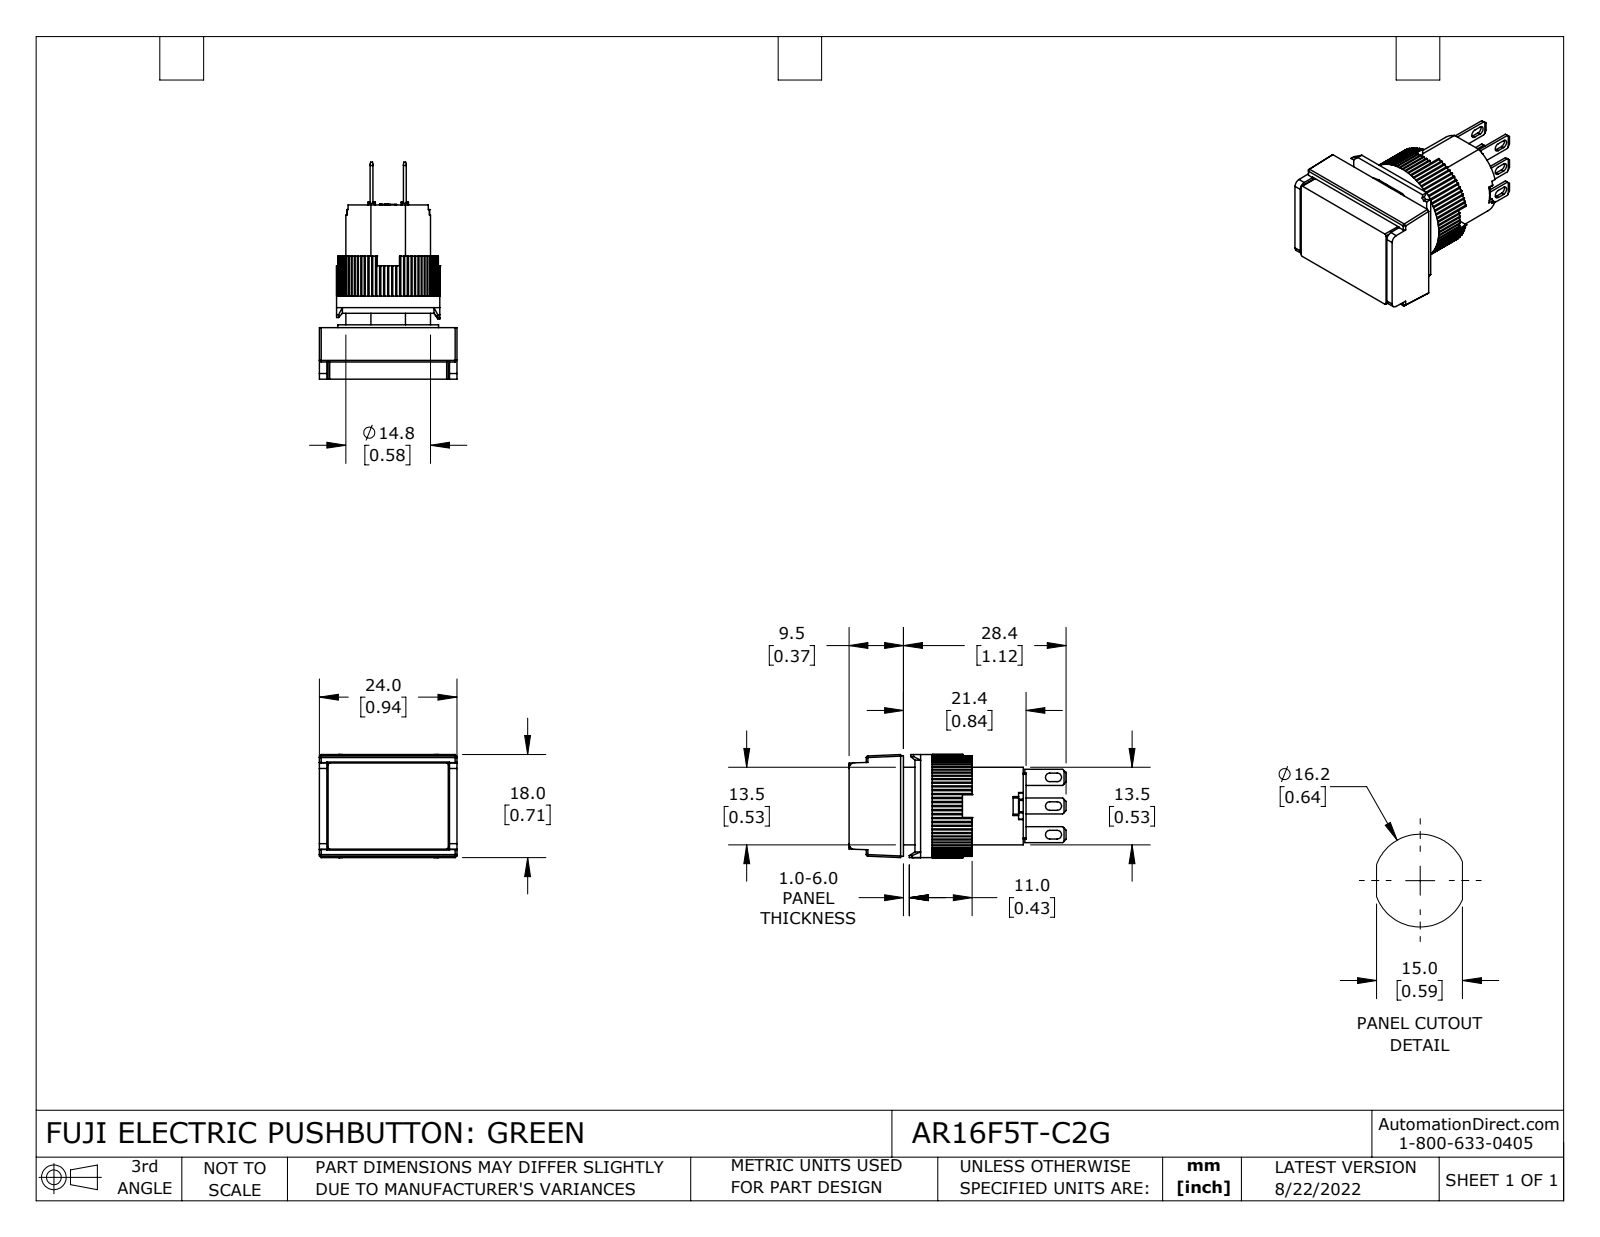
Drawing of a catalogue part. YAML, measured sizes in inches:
part_name: "AR16F5T-C2G"
step_written_by: "SolidWorks 2021 (CONFIG_CONTROL_DESIGN)"
units: inches
bodies: {solids: 12, faces: 813, planar: 632, cylindrical: 177, other: 4}
overall_size: [1.492, 0.945, 0.709]
volume: 0.443
surface_area: 9.124
round_holes:
  - {diameter: 0.543, count: 1}
  - {diameter: 0.583, count: 1}
round_bosses_or_shafts:
  - {diameter: 0.709, count: 1}
  - {diameter: 0.693, count: 1}
partial_cylinders:
  - {radius: 0.01, count: 80}
  - {radius: 0.008, count: 12}
  - {radius: 0.012, count: 6}
  - {radius: 0.03, count: 6}
  - {radius: 0.039, count: 2}
face_to_face_distances: [0.213, 0.354, 0.142, 0.492, 0.35, 0.138, 0.02, 0.843, 0.059, 0.453]
